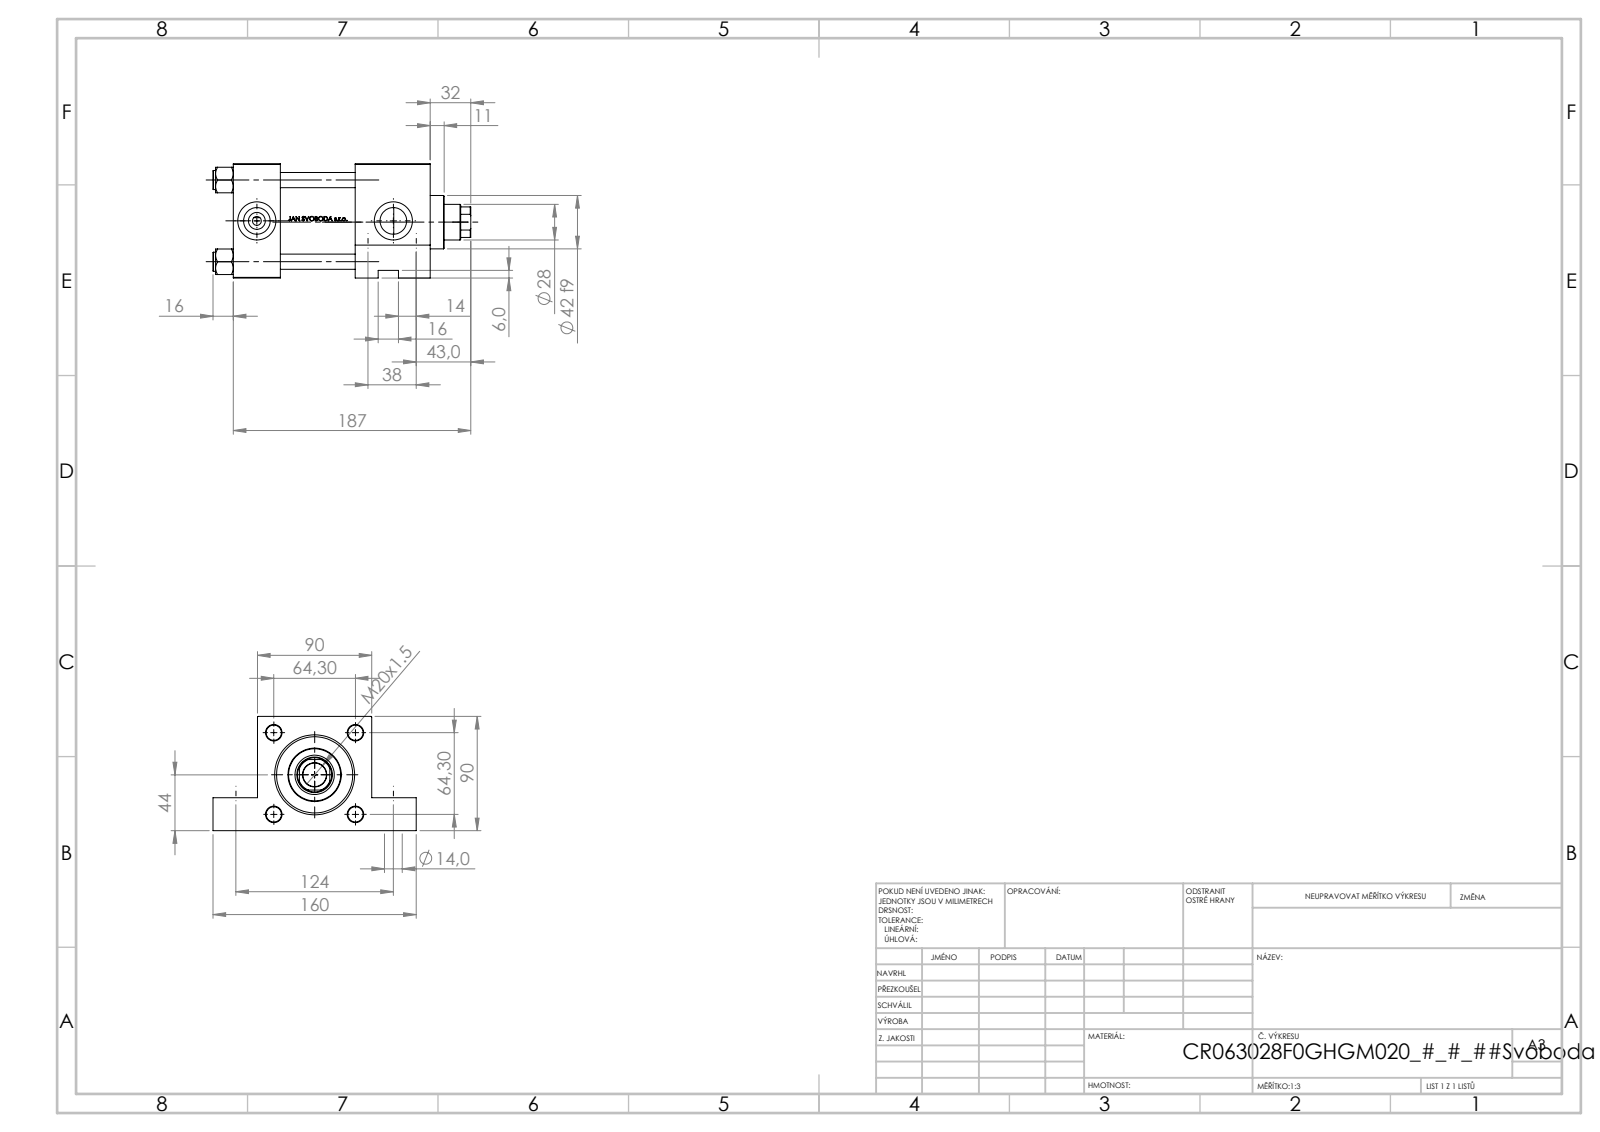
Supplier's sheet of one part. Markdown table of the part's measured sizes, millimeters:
| quantity | value |
| --- | --- |
| part name | V215CR_F_Body; NUT_M5_F; V215CR_F_TYCINKA; V215CR_VCP_F (+1 more) |
| STEP written by | SolidWorks 2019 (CONFIG_CONTROL_DESIGN) |
| units | millimeters |
| bodies | 11 solids, 1103 faces (437 planar, 126 cylindrical, 540 other) |
| overall size | 203 × 160 × 90 |
| volume | 1 030 000 mm³ |
| surface area | 193 787 mm² |
| round holes (diameter × count) | 12 × 4, 7 × 2, 14 × 2, 14 × 2, 20.96 × 2, 30 × 2, 18.5 × 1, 28 × 1, 31 × 1, 50 × 1, 60 × 1, 63 × 1 |
| round bosses / shafts (diameter × count) | 15 × 4, 69 × 1, 42 × 1 |
| partial cylindrical surfaces (radius × count) | 13.5 × 1 |
| main face-to-face distances | 90, 59, 37, 155, 118, 96, 20, 26, 64, 125 |
| hole center spacings | 64.3, 38, 44.77, 46.18, 90.93, 124, 129.69, 107.5 |
